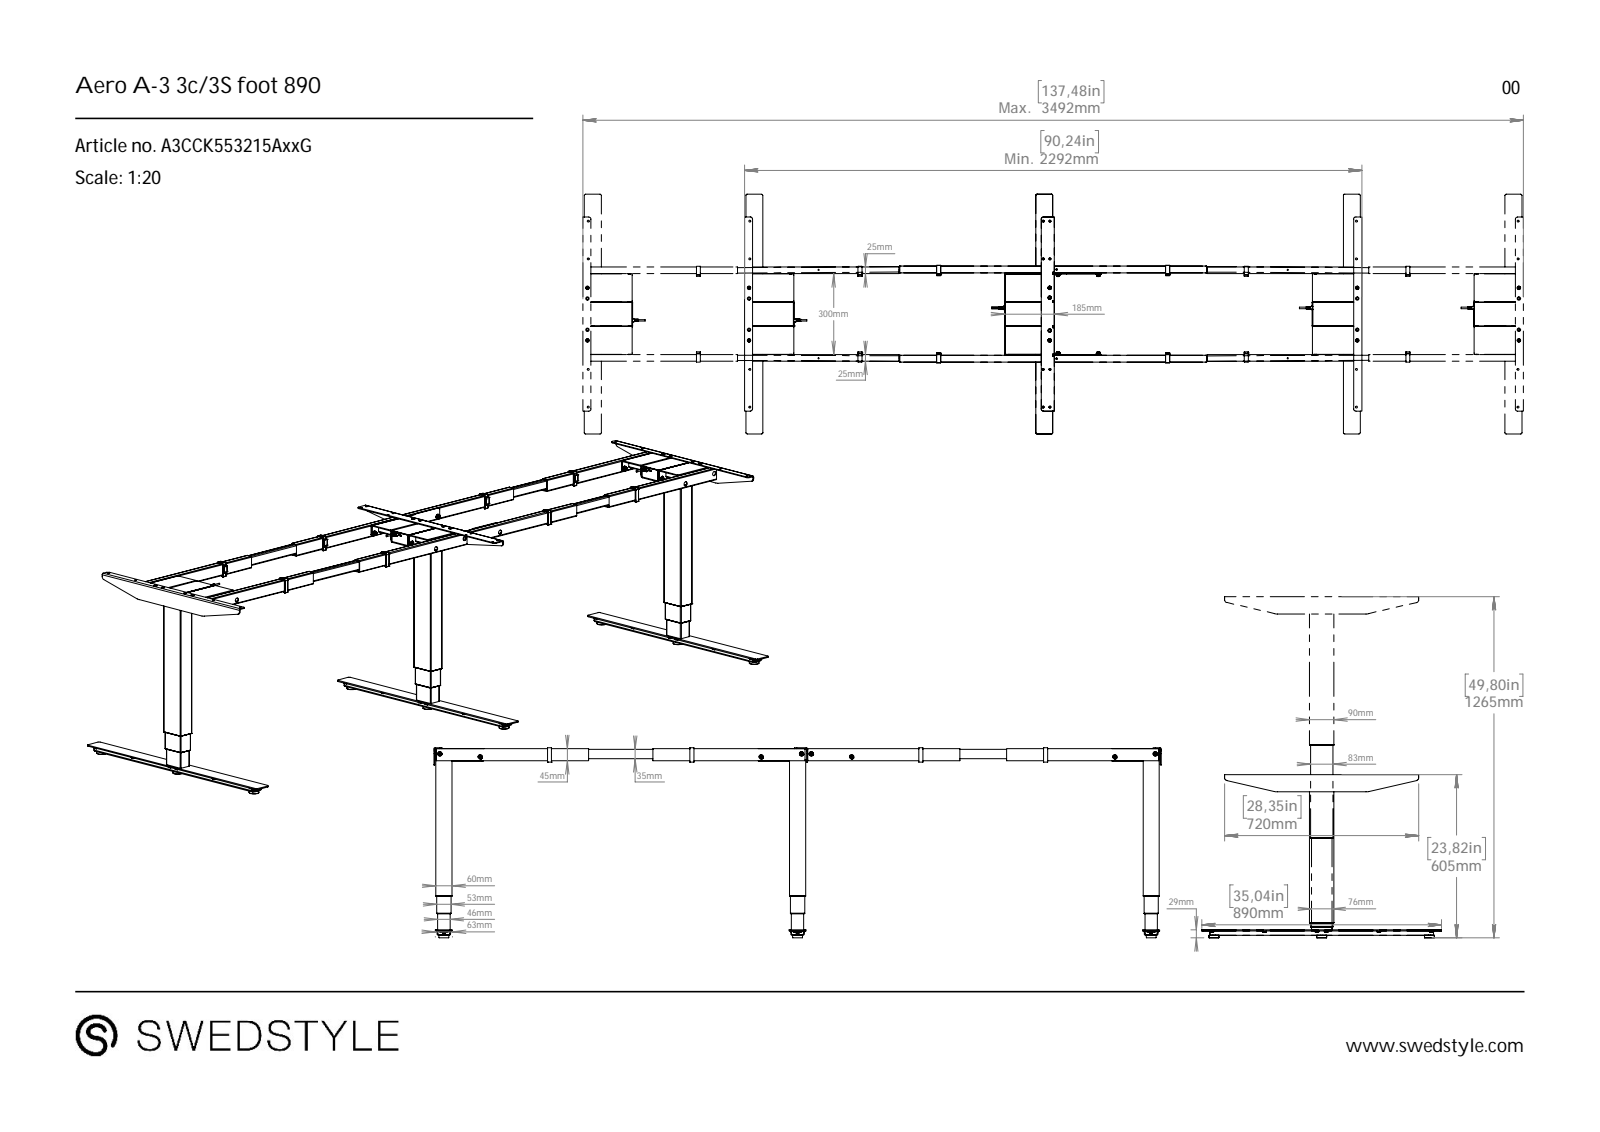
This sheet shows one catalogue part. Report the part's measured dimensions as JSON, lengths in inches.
{"part_name": "A3CCK553215AxxG Aero A-3 3c_3S foot 890", "step_written_by": "SolidWorks 2021 (CONFIG_CONTROL_DESIGN)", "units": "inches", "bodies": {"solids": 0, "faces": 1587, "planar": 746, "cylindrical": 542, "other": 299}, "overall_size": [106.299, 35.039, 27.756], "round_holes": [[0.63, 18], [0.276, 16], [0.197, 6], [0.213, 3], [0.315, 3], [0.165, 2]], "round_bosses_or_shafts": [[0.236, 4], [0.335, 2], [0.315, 2], [0.217, 2], [0.613, 1]], "partial_cylinders_radius": [[0.098, 108], [0.118, 32], [0.197, 25], [0.02, 18], [0.138, 16], [0.059, 13], [0.079, 9], [0.11, 9]], "face_to_face_distances": [0.079, 0.118, 51.693, 0.138, 0.272, 0.134, 0.787, 0.906, 12.913, 103.386], "hole_center_spacings": [5.512, 21.654, 102.798, 0.984, 1.678, 5.599, 6.82, 7.186]}
